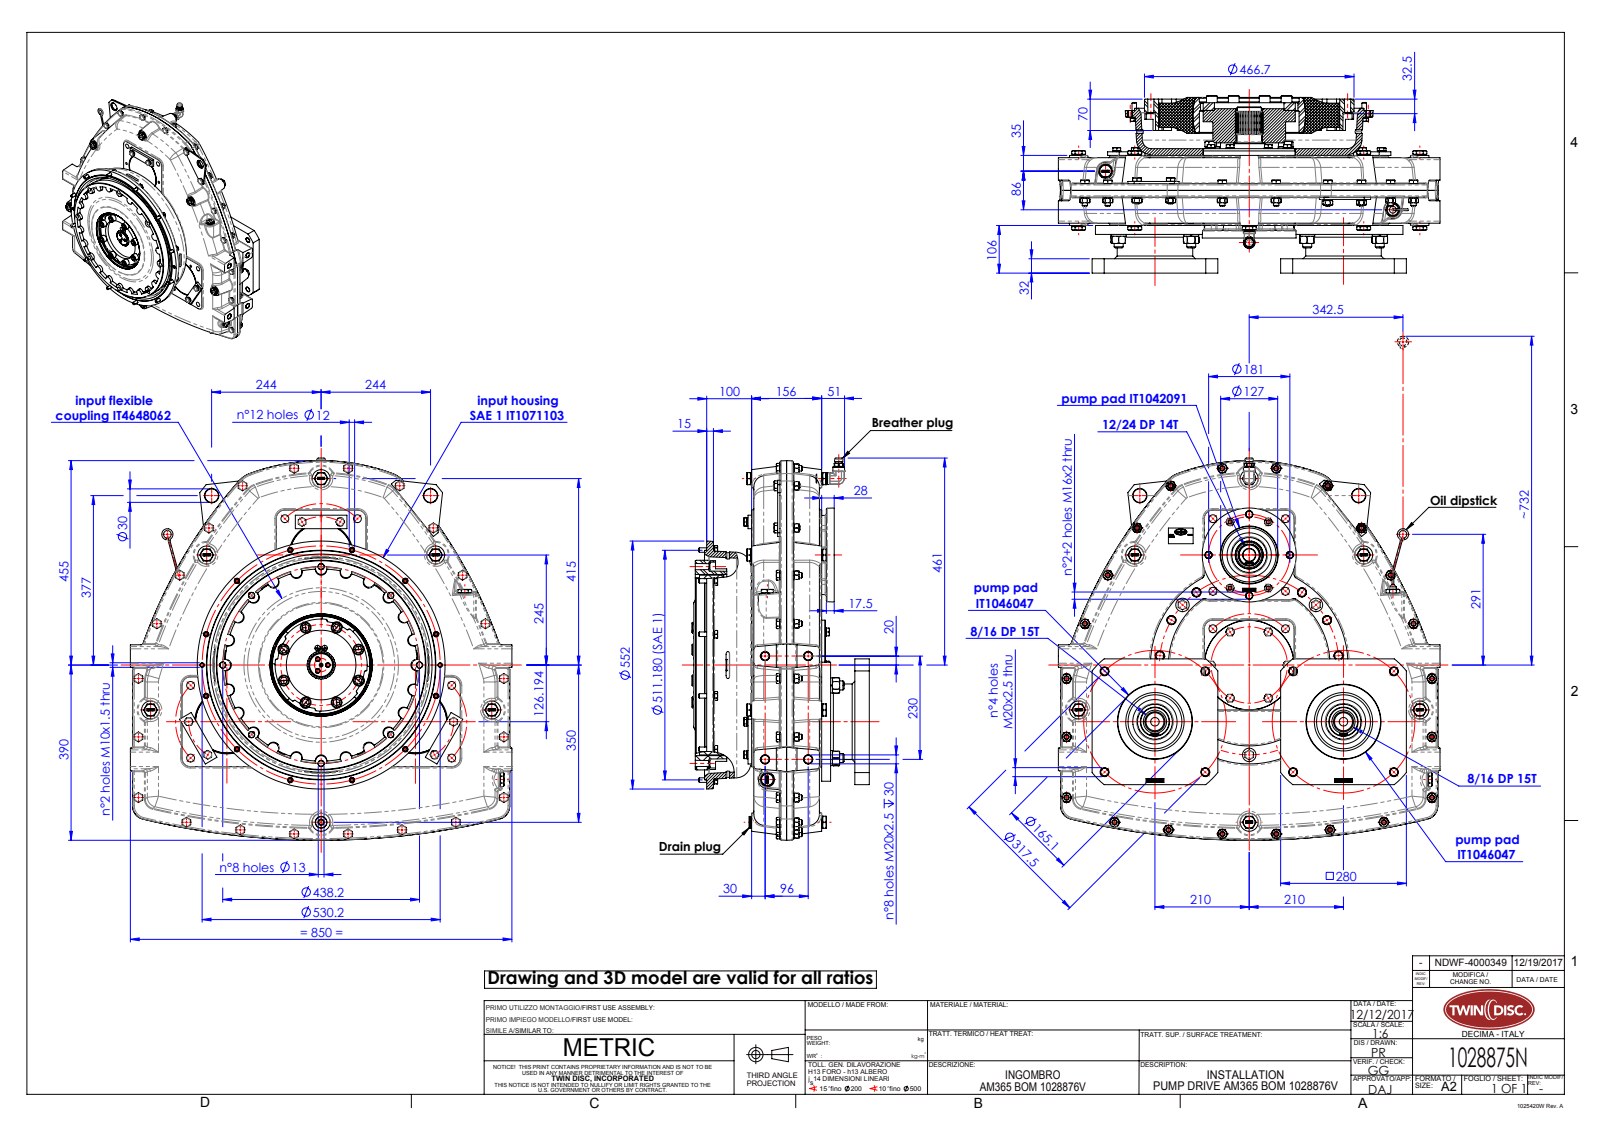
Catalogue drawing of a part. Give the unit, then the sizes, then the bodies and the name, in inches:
Units: inches
Overall size (bounding box): 33.496 × 33.465 × 15.559
Round holes (diameter × count): ⌀0.689 ×38, ⌀0.512 ×36, ⌀0.335 ×29, ⌀0.827 ×26, ⌀0.48 ×25, ⌀0.402 ×24, ⌀0.406 ×21, ⌀0.472 ×19, ⌀0.551 ×16, ⌀0.795 ×16, ⌀0.433 ×14, ⌀0.669 ×13
Round bosses / shafts (diameter × count): ⌀0.394 ×29, ⌀0.831 ×25, ⌀0.709 ×25, ⌀0.787 ×24, ⌀0.713 ×24, ⌀0.638 ×24, ⌀0.472 ×21, ⌀1.323 ×16
Partial cylindrical surfaces — rounded edges, fillets, slot ends (radius × count): R0.492 ×72, R0.014 ×58, R0.018 ×58, R1.04 ×58, R1.163 ×58, R0.118 ×56, R0.079 ×54, R0.098 ×46
Main face-to-face distances: 3.071, 2.874, 5.945, 0.197, 3.661, 0.591, 5.748, 6.142, 0.787, 6.732
Hole centre spacings: 13.638, 32.047, 3.274, 11.703, 9.257, 1.783, 2.591, 2.953
Volume: 5 761 in³ · Surface area: 11 440 in²
Bodies: 185 solids, 10464 faces (4356 planar, 2788 cylindrical, 3320 other)
Part name (STEP PRODUCT): ITam365-006_rev00-installation; ITam365-005_rev00-installation; IT4648062_rev00-installation; IT1071103_rev02-installation (+8 more)
STEP written by: SolidWorks 2015 (AUTOMOTIVE_DESIGN)
